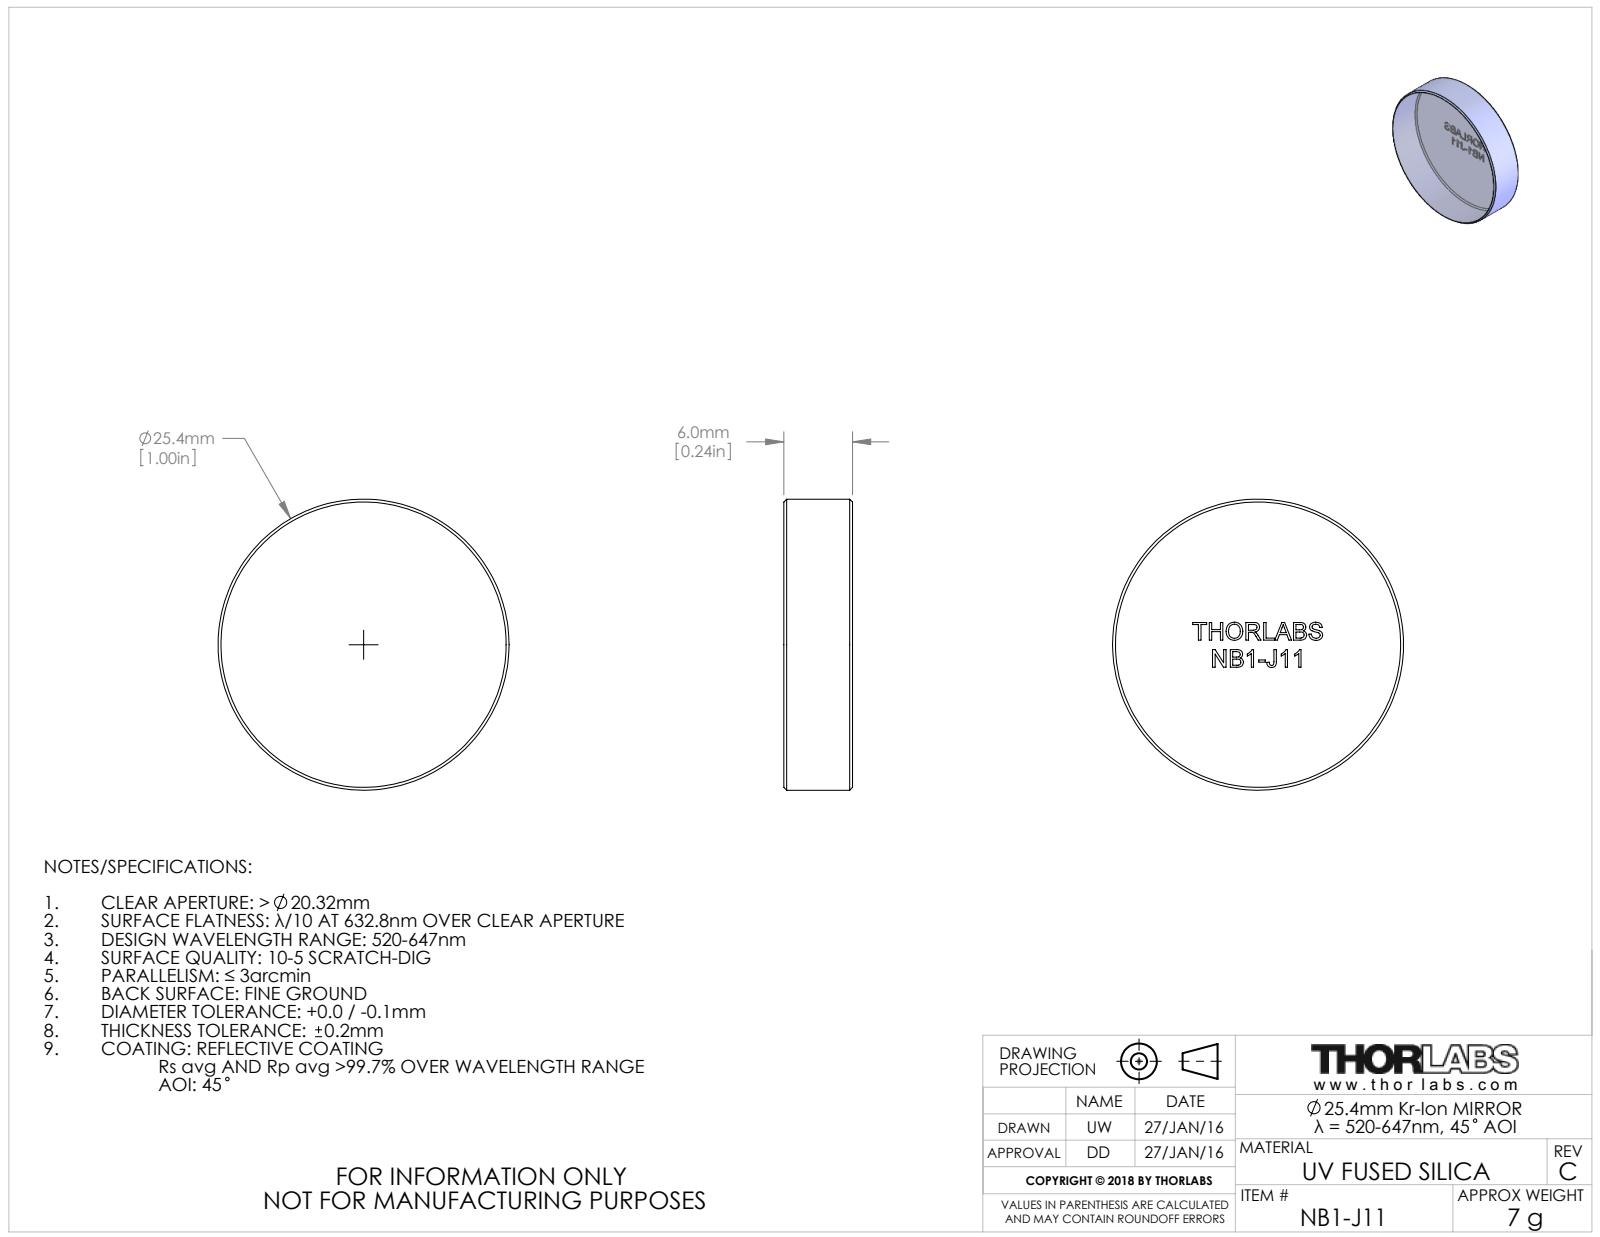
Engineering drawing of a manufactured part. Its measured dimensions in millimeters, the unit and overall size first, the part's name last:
Units: millimetres
Overall size (bounding box): 25.4 × 25.4 × 6
Round bosses / shafts (diameter × count): ⌀25.4 ×1
Main face-to-face distances: 6, 1.5, 4.1, 2.4, 2.4, 1.2, 0.5, 1.9, 1.4, 0.7
Volume: 3 030 mm³ · Surface area: 1 468 mm²
Bodies: 1 solid, 193 faces (125 planar, 2 cylindrical, 66 other)
Part name (STEP PRODUCT): 8660-E0W
STEP written by: SolidWorks 2009 (AUTOMOTIVE_DESIGN)
